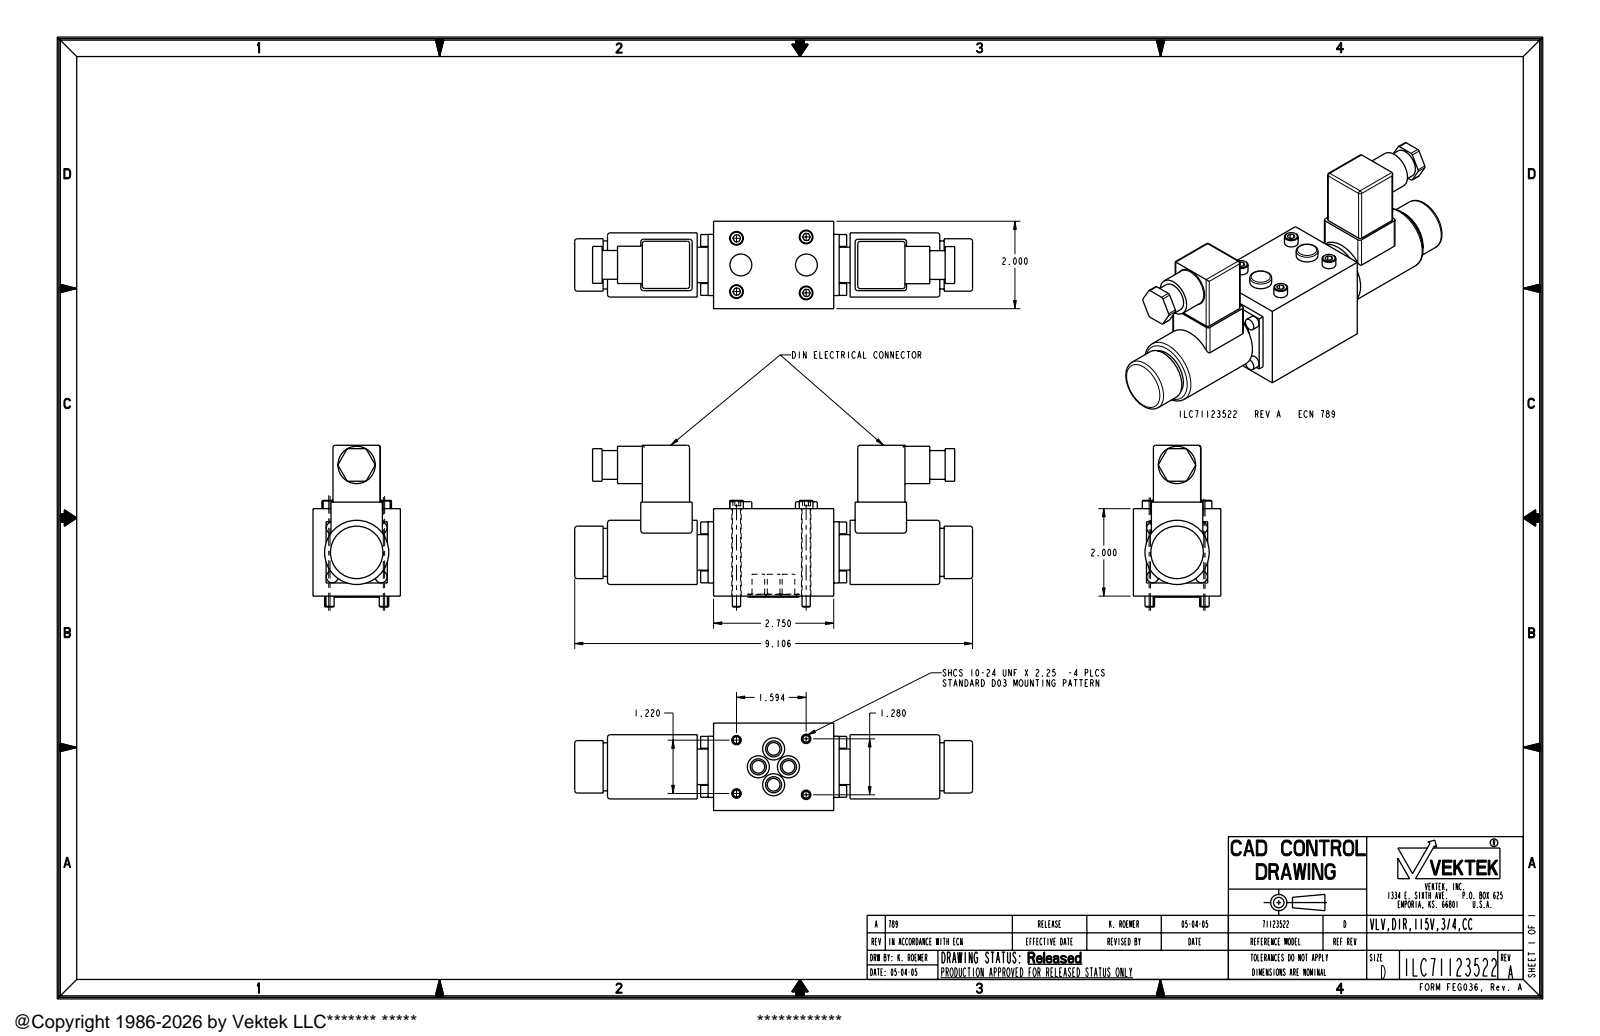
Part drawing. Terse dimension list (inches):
name: ILC71123522
written by: PRO/ENGINEER BY PARAMETRIC TECHNOLOGY CORPORATION, 2004290 (AUTOMOTIVE_DESIGN_CC2)
unit: in
bodies: 1 solid, 282 faces (120 planar, 118 cylindrical, 44 other)
size: 9.106 × 3.7 × 2
volume: 25.88 in³; area: 100.3 in²
holes: 4× ⌀0.215, 4× ⌀0.29, 4× ⌀0.49
bosses: 4× ⌀0.313, 4× ⌀0.272, 4× ⌀0.187, 2× ⌀0.854, 2× ⌀0.658, 2× ⌀0.5, 1× ⌀1.469, 1× ⌀1.2
rounds: 26× R0.05, 8× R0.06
face distances: 2, 1.08, 0.412, 1.588, 0.55, 0.125, 0.458, 0.462, 1.538, 1.542
hole spacings: 0.532, 0.539, 0.757, 0.779, 0.789, 0.873, 1.268, 1.287
